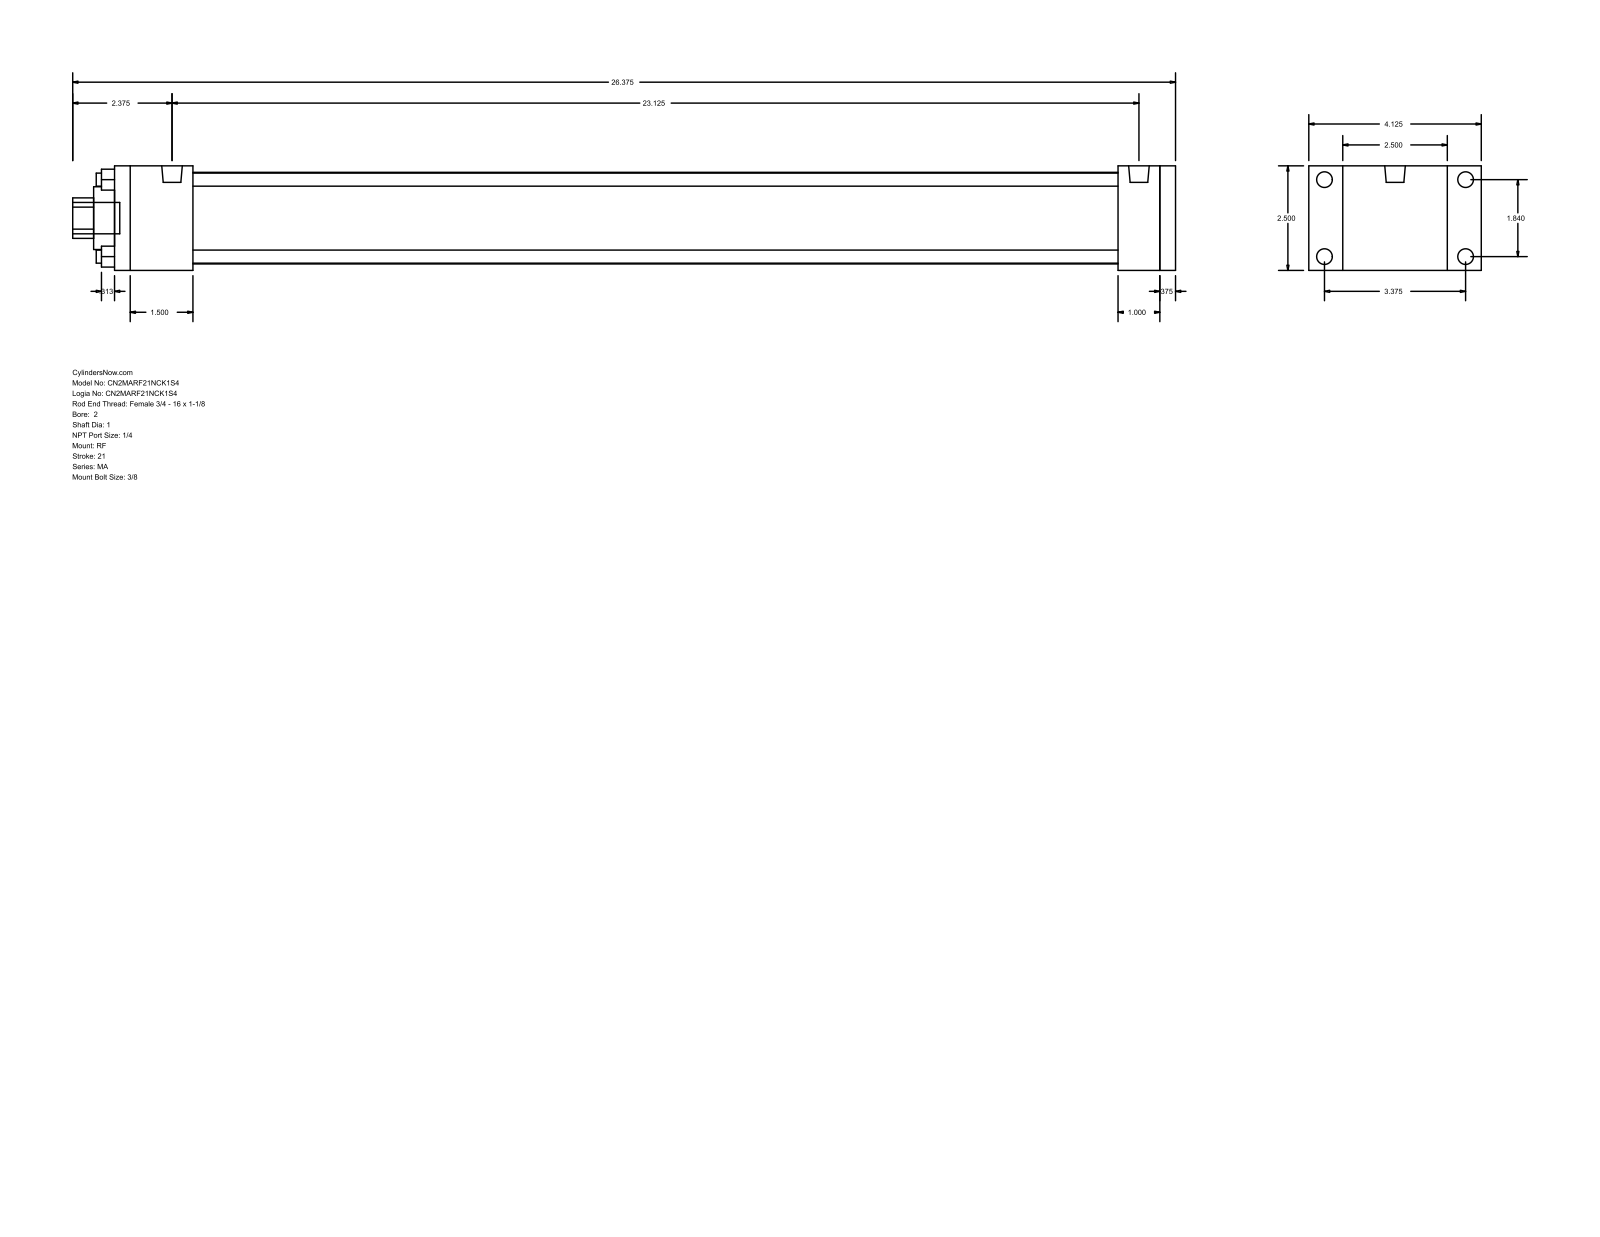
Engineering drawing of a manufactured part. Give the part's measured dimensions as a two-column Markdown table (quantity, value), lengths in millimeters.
| quantity | value |
| --- | --- |
| part name | MA_RF__0200_1 |
| STEP written by | GSSL Pune (CONFIG_CONTROL_DESIGN) |
| units | millimeters |
| bodies | 0 solids, 92 faces (64 planar, 28 cylindrical, 0 other) |
| overall size | 669.92 × 104.78 × 63.5 |
| round holes (diameter × count) | 7.94 × 4, 25.4 × 1, 38.1 × 1, 55.63 × 1 |
| round bosses / shafts (diameter × count) | 9.53 × 4, 7.94 × 4, 12.49 × 2, 19.05 × 1 |
| partial cylindrical surfaces (radius × count) | 12.29 × 1 |
| main face-to-face distances | 63.5, 635, 9.52, 644.52, 25.4, 20.64, 12.7, 47.63, 587.37, 596.89 |
| hole center spacings | 33.05, 46.74, 66.1 |
